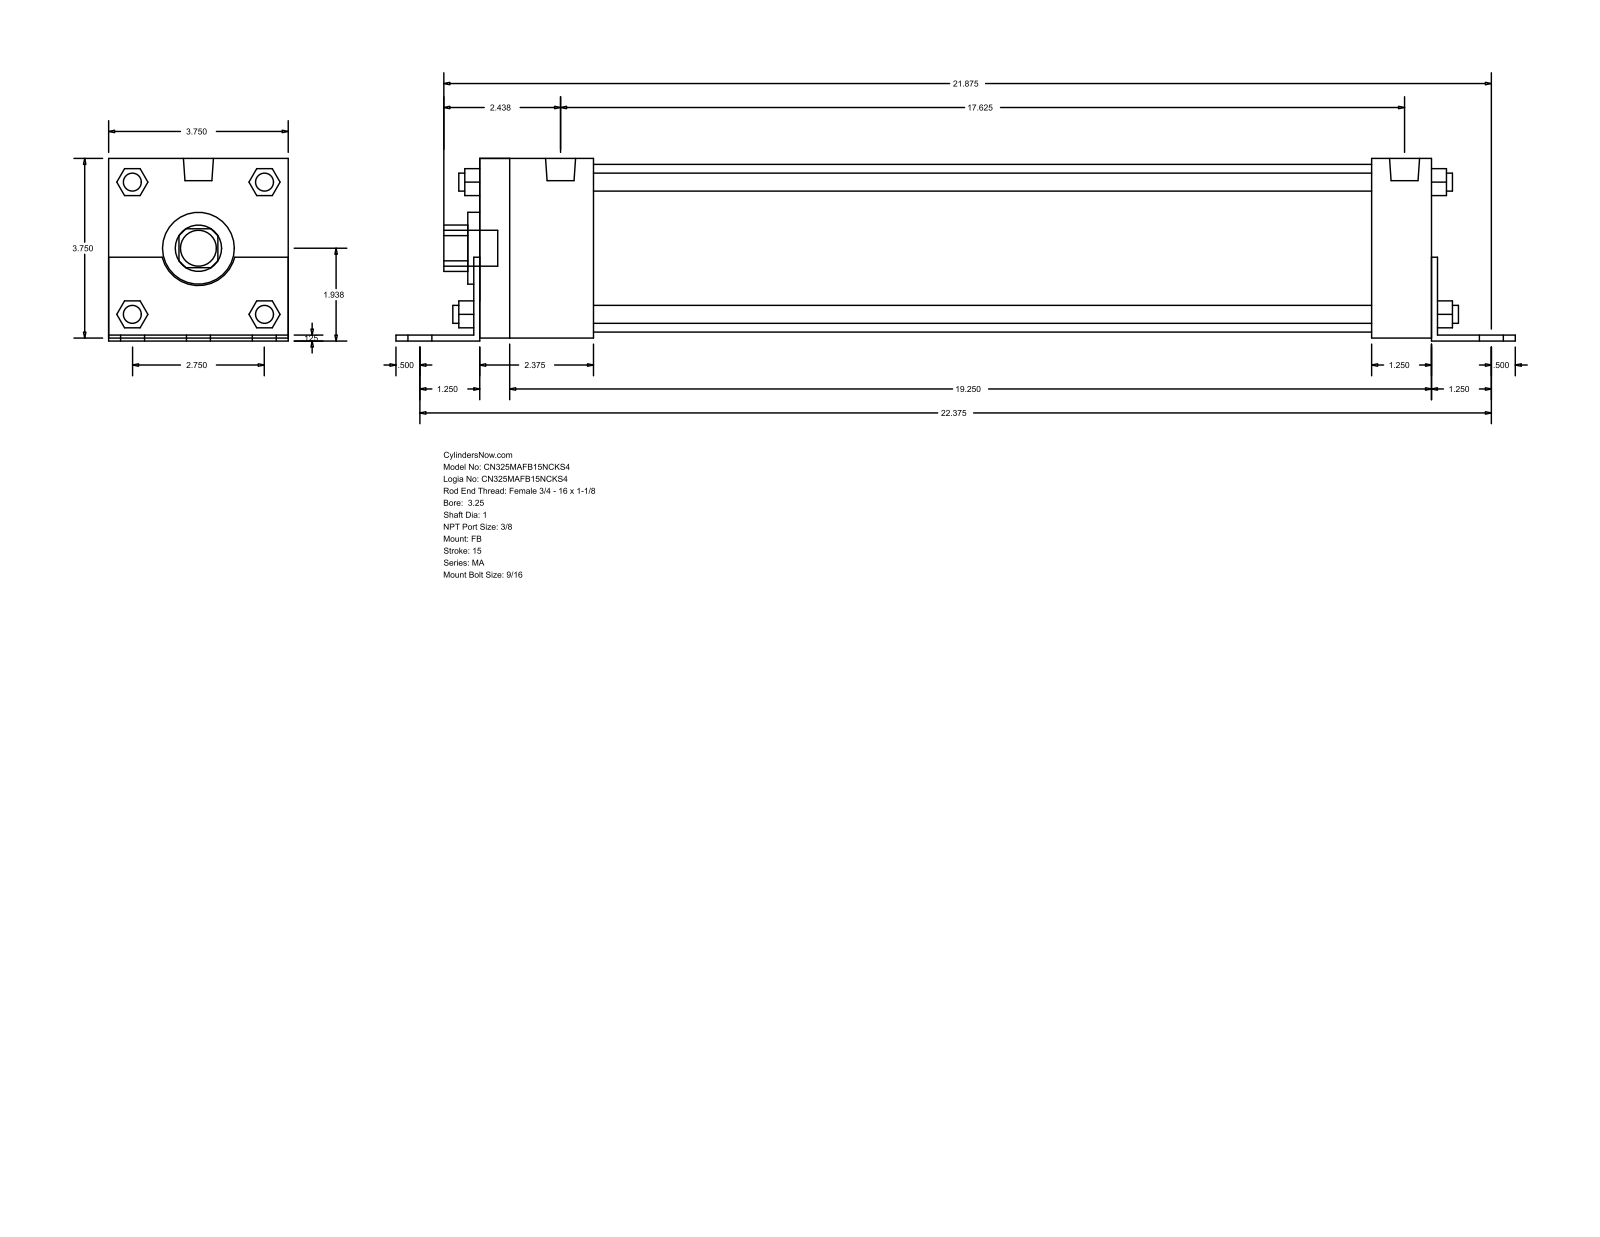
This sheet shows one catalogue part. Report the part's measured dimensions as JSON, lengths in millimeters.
{"part_name": "MA_FB__0325_1", "step_written_by": "GSSL Pune (CONFIG_CONTROL_DESIGN)", "units": "millimeters", "bodies": {"solids": 0, "faces": 140, "planar": 105, "cylindrical": 35, "other": 0}, "overall_size": [593.73, 96.84, 95.25], "round_holes": [[25.4, 1], [38.1, 1], [88.9, 1]], "round_bosses_or_shafts": [[14.29, 6], [11.11, 4], [9.53, 4], [15.93, 2], [19.05, 1]], "partial_cylinders_radius": [[12.29, 1], [19.81, 1]], "face_to_face_distances": [95.24, 3.17, 1.59, 96.83, 1.58, 93.66, 508, 504.83, 511.17, 34.93]}
